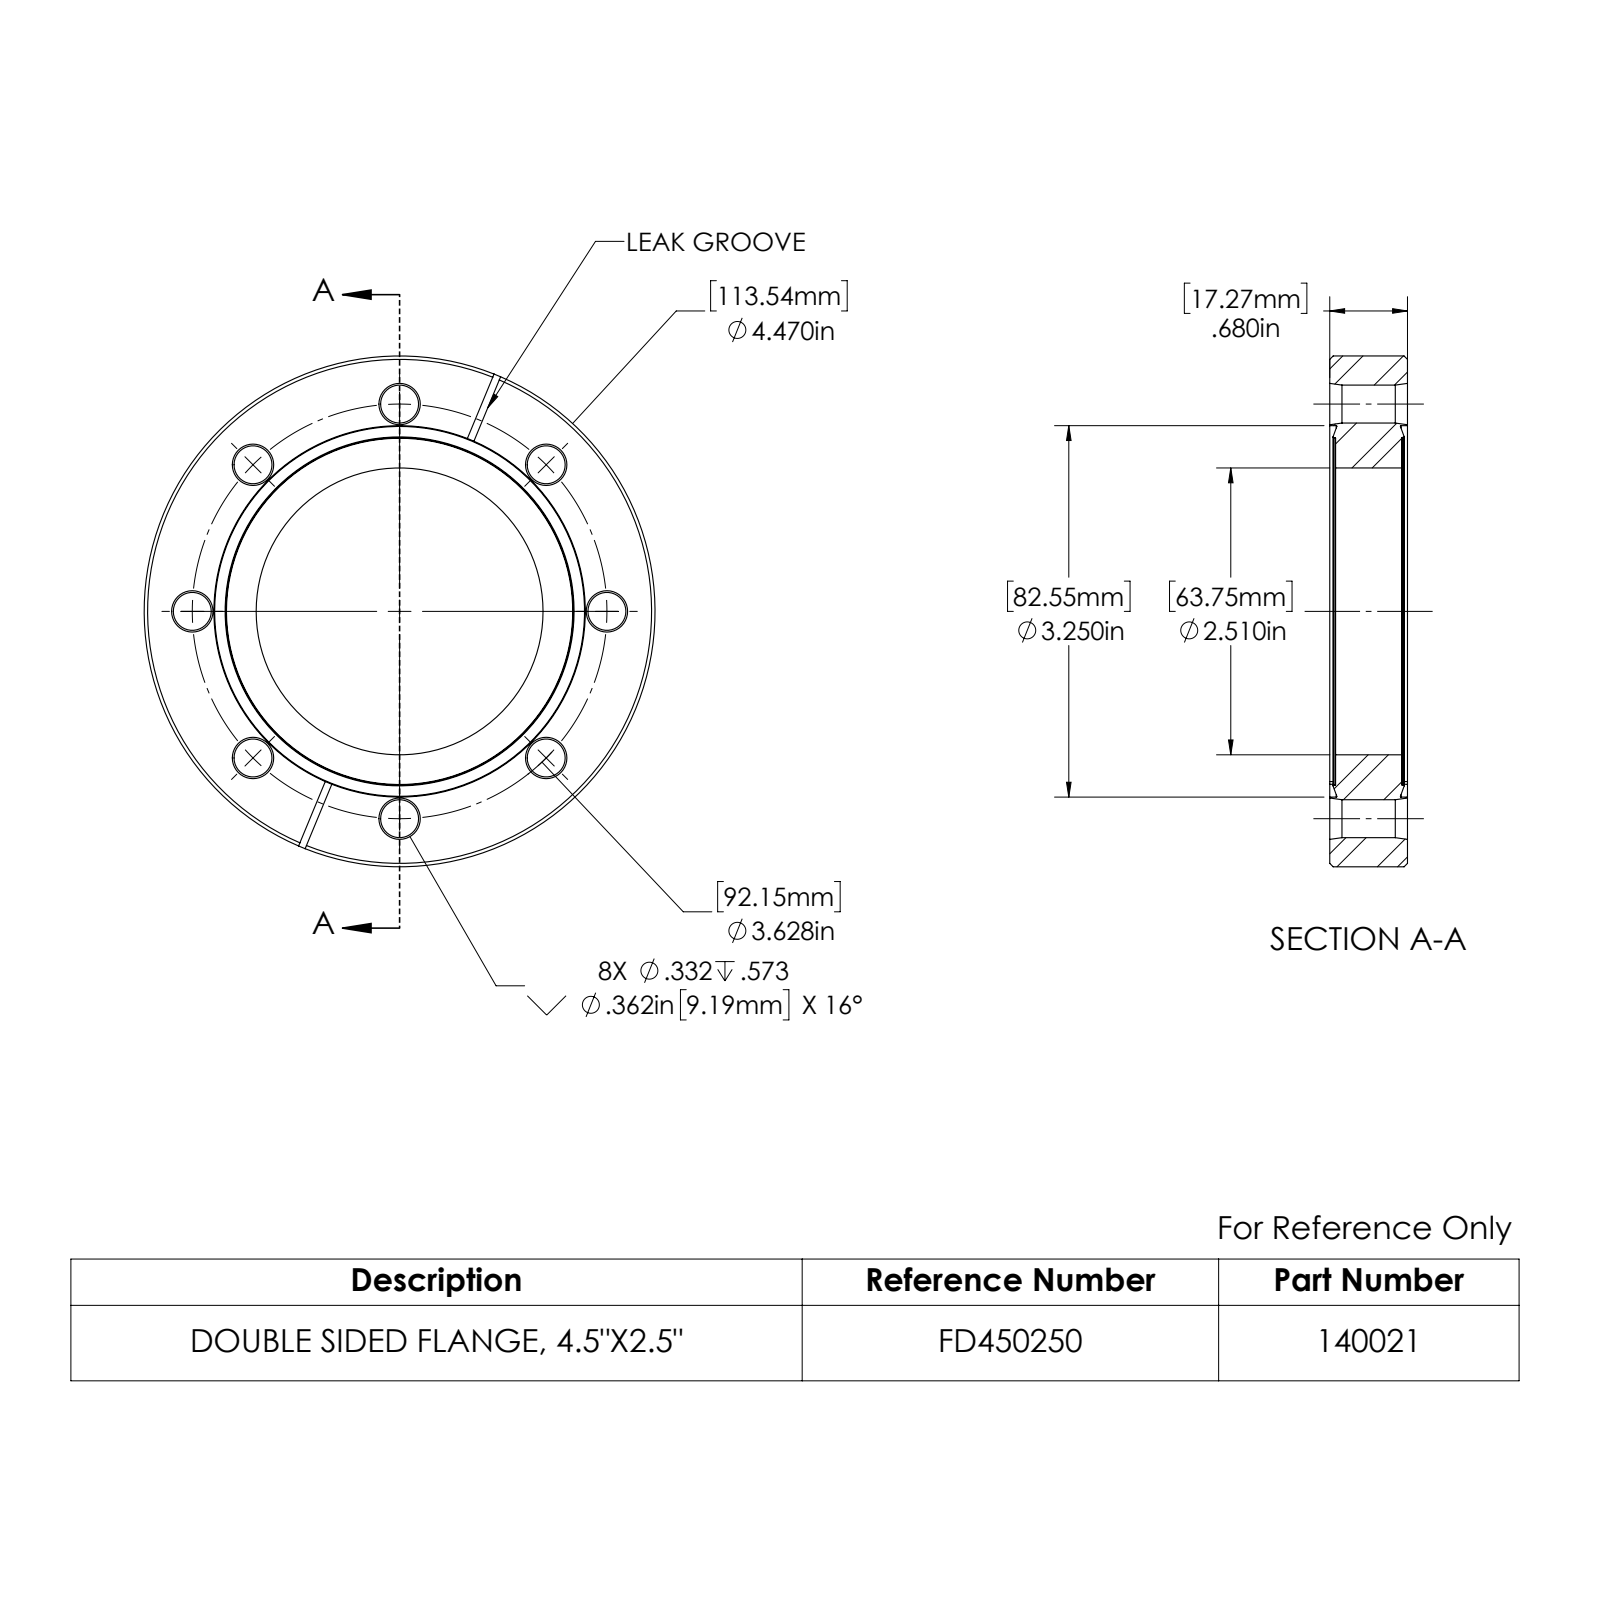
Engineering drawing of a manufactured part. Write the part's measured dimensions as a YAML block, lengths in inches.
part_name: "140021_A"
step_written_by: "SolidWorks 2022 (CONFIG_CONTROL_DESIGN)"
units: inches
bodies: {solids: 1, faces: 100, planar: 14, cylindrical: 32, other: 54}
overall_size: [4.47, 4.47, 0.68]
volume: 6.461
surface_area: 41.47
round_holes:
  - {diameter: 0.332, count: 8}
  - {diameter: 2.51, count: 1}
  - {diameter: 3.04, count: 1}
  - {diameter: 3.25, count: 1}
round_bosses_or_shafts:
  - {diameter: 4.47, count: 1}
partial_cylinders:
  - {radius: 1.25, count: 4}
face_to_face_distances: [0.68, 0.629, 0.051, 0.051, 0.578, 0.629, 0.062, 0.061, 0.063]
hole_center_spacings: [1.389, 1.814, 3.352, 2.565, 2.566, 3.628, 3.628]
